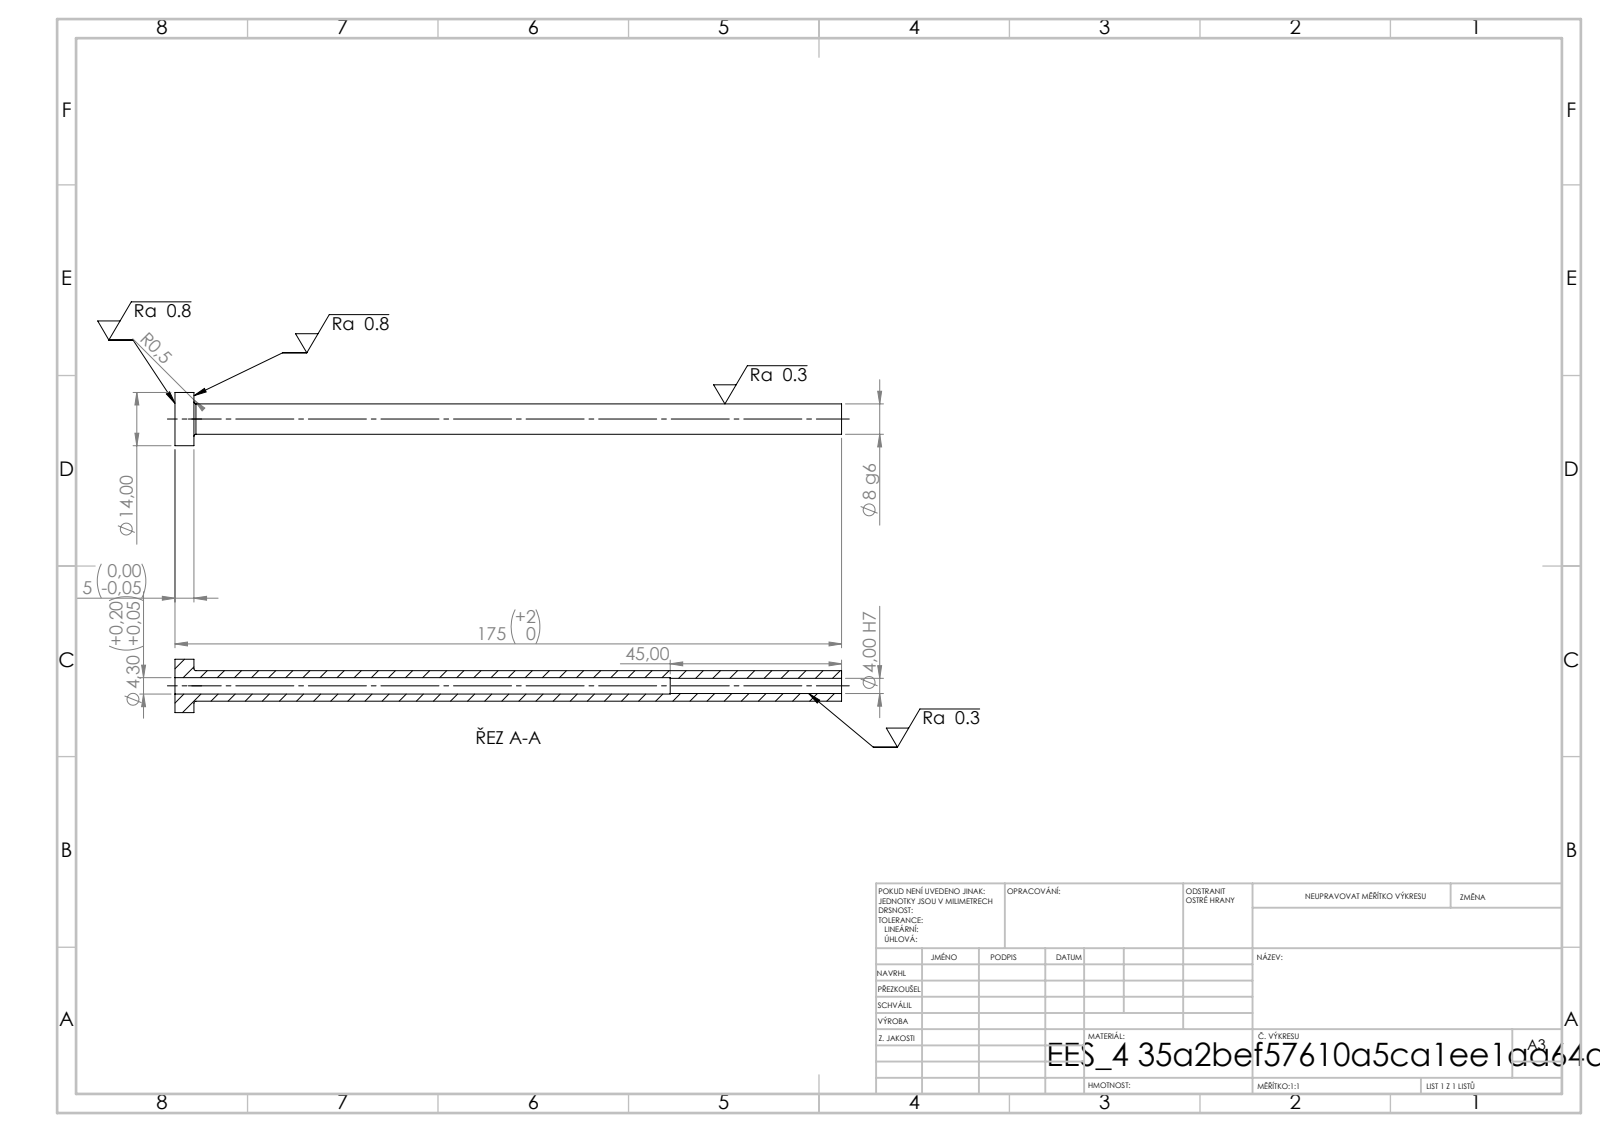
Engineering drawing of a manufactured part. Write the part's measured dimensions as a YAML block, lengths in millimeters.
step_written_by: "SolidWorks 2019 (CONFIG_CONTROL_DESIGN)"
units: millimeters
bodies: {solids: 1, faces: 14, planar: 4, cylindrical: 8, other: 2}
overall_size: [175, 14, 14]
volume: 6863
surface_area: 7092
round_holes:
  - {diameter: 4, count: 1}
  - {diameter: 4.3, count: 1}
round_bosses_or_shafts:
  - {diameter: 14, count: 1}
  - {diameter: 8, count: 1}
face_to_face_distances: [5, 175, 170, 130, 125, 45]
